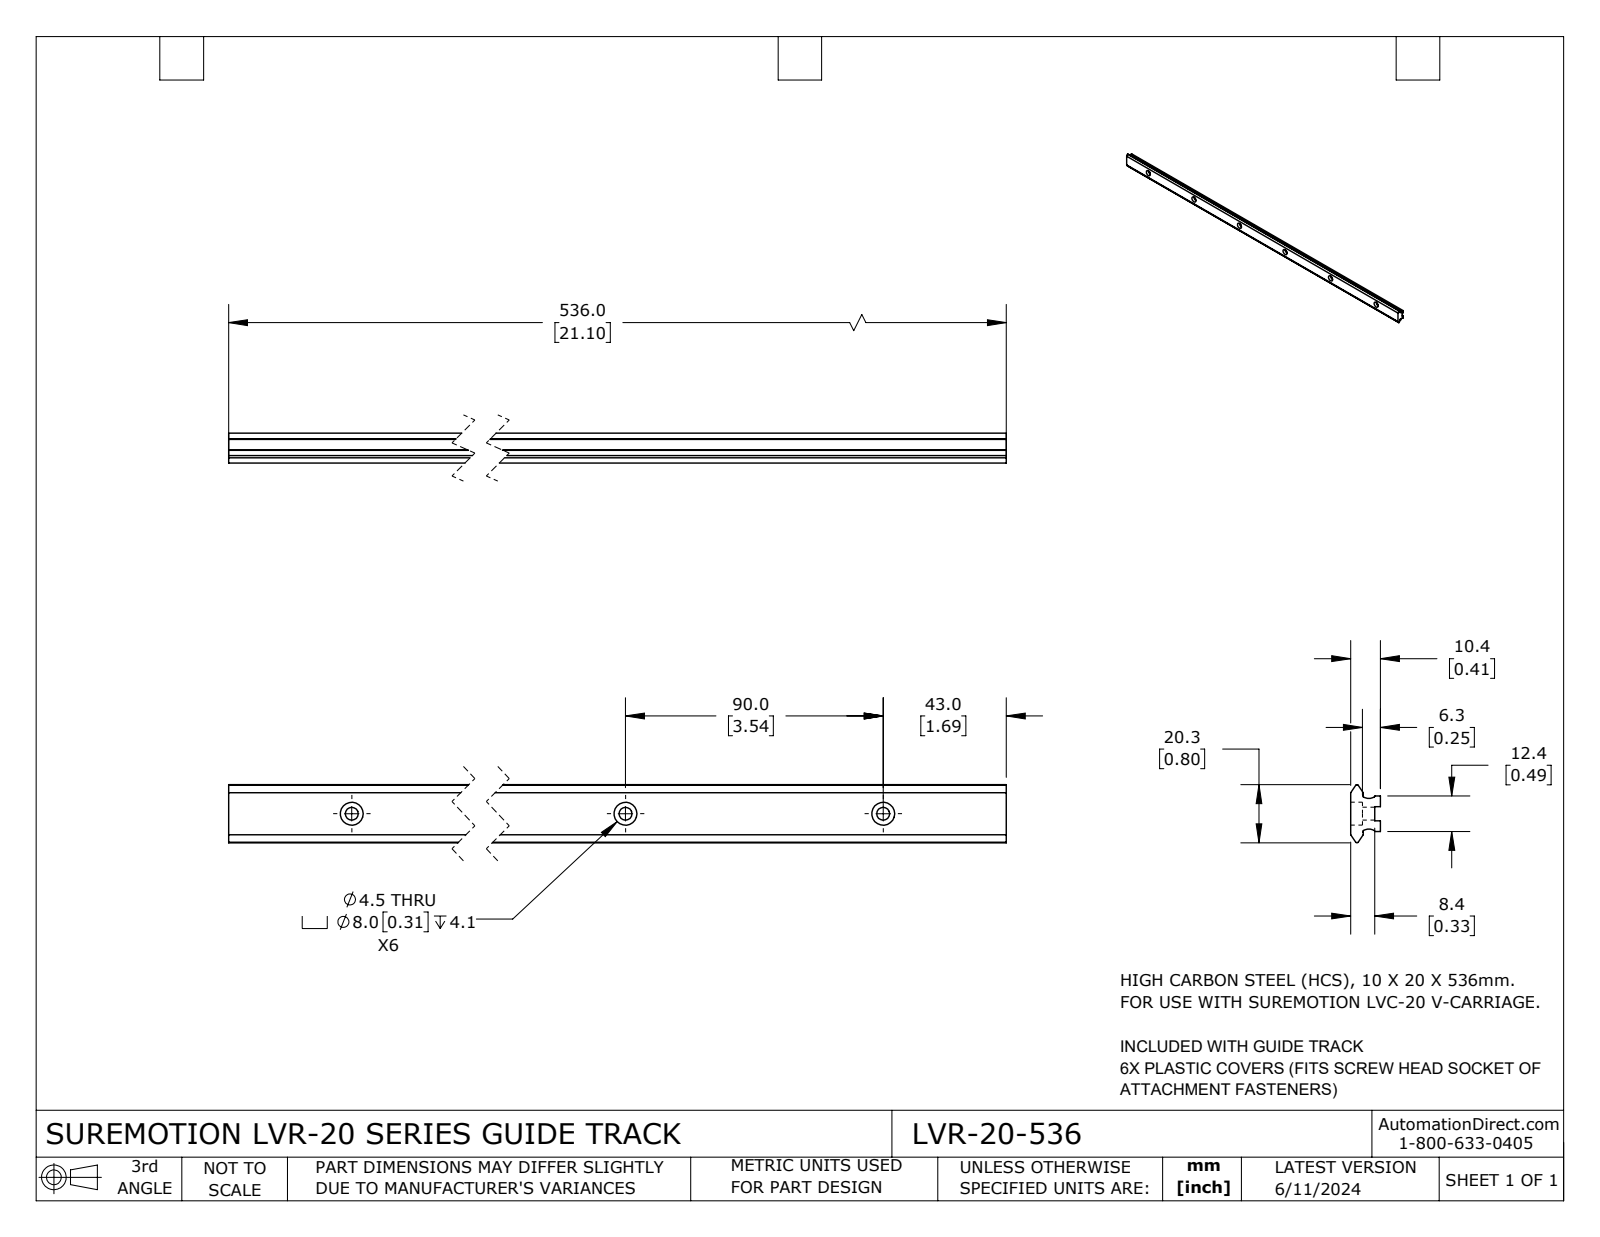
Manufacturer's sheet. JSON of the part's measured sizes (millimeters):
{"part_name": "LVR-20-536", "step_written_by": "SolidWorks 2023 (CONFIG_CONTROL_DESIGN)", "units": "millimeters", "bodies": {"solids": 1, "faces": 56, "planar": 22, "cylindrical": 34, "other": 0}, "overall_size": [536, 20.27, 10.41], "volume_mm3": 72037, "surface_area_mm2": 34031, "round_holes": [[4.5, 6], [8, 6]], "partial_cylinders_radius": [[0.4, 4], [0.5, 2], [3.84, 2]], "face_to_face_distances": [10.41, 2, 8.41, 3.7, 8.7, 12.06, 12.05, 5, 12.4, 5.99], "hole_center_spacings": [90, 180, 270, 360, 450]}
